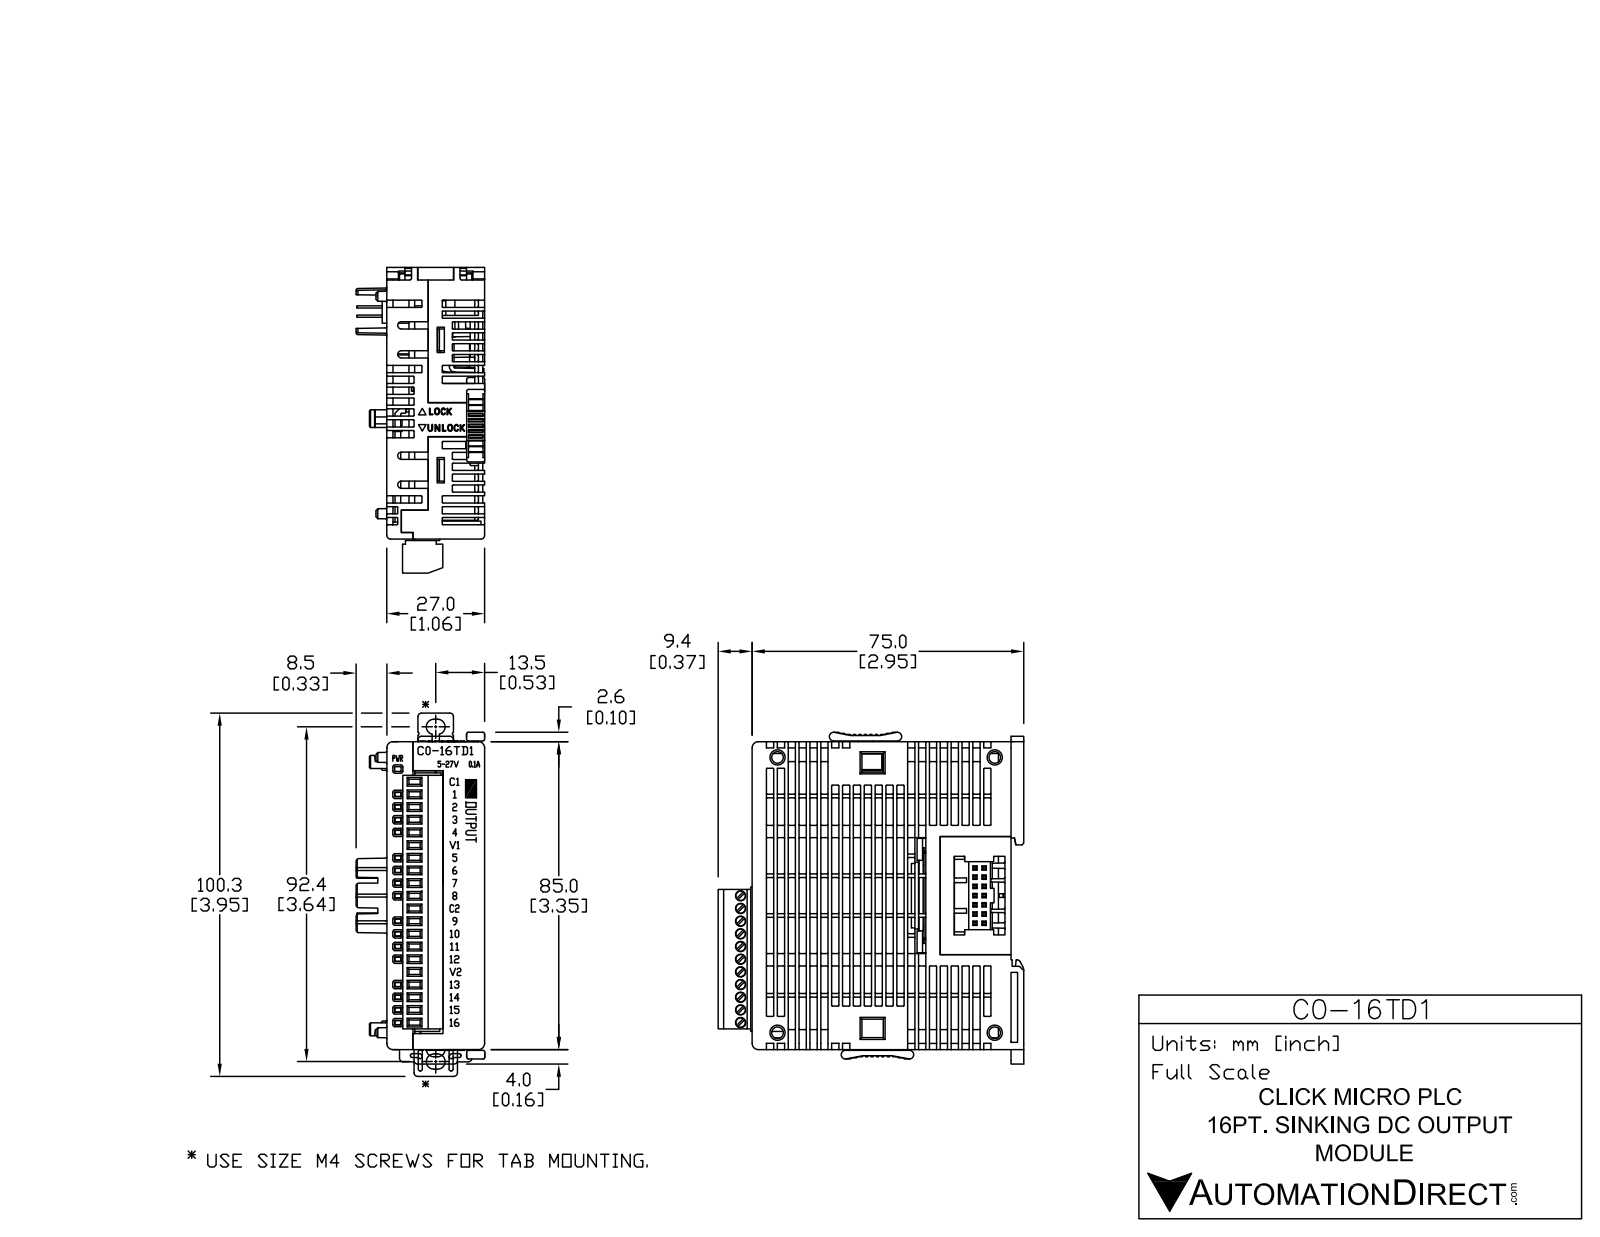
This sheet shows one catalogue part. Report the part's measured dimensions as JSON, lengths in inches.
{"part_name": "C0-16TD1", "step_written_by": "SolidWorks 2009 (AUTOMOTIVE_DESIGN)", "units": "inches", "bodies": {"solids": 1, "faces": 3989, "planar": 2836, "cylindrical": 1037, "other": 116}, "overall_size": [3.606, 3.323, 1.4], "volume_in3": 10.07, "surface_area_in2": 52.1, "round_holes": [[0.039, 20], [0.11, 20], [0.126, 4], [0.079, 2]], "round_bosses_or_shafts": [[0.102, 20], [0.075, 1]], "partial_cylinders_radius": [[0.008, 570], [0.02, 43], [0.012, 22], [0.11, 20], [0.039, 18], [0.047, 12], [0.067, 6], [0.083, 4]], "face_to_face_distances": [0.02, 1.063, 0.02, 1.043, 2.815, 3.346, 0.067, 1.035, 1.056, 0.138], "hole_center_spacings": [0.138, 0.276, 0.413, 0.551, 0.689, 0.827, 0.965, 1.102]}
